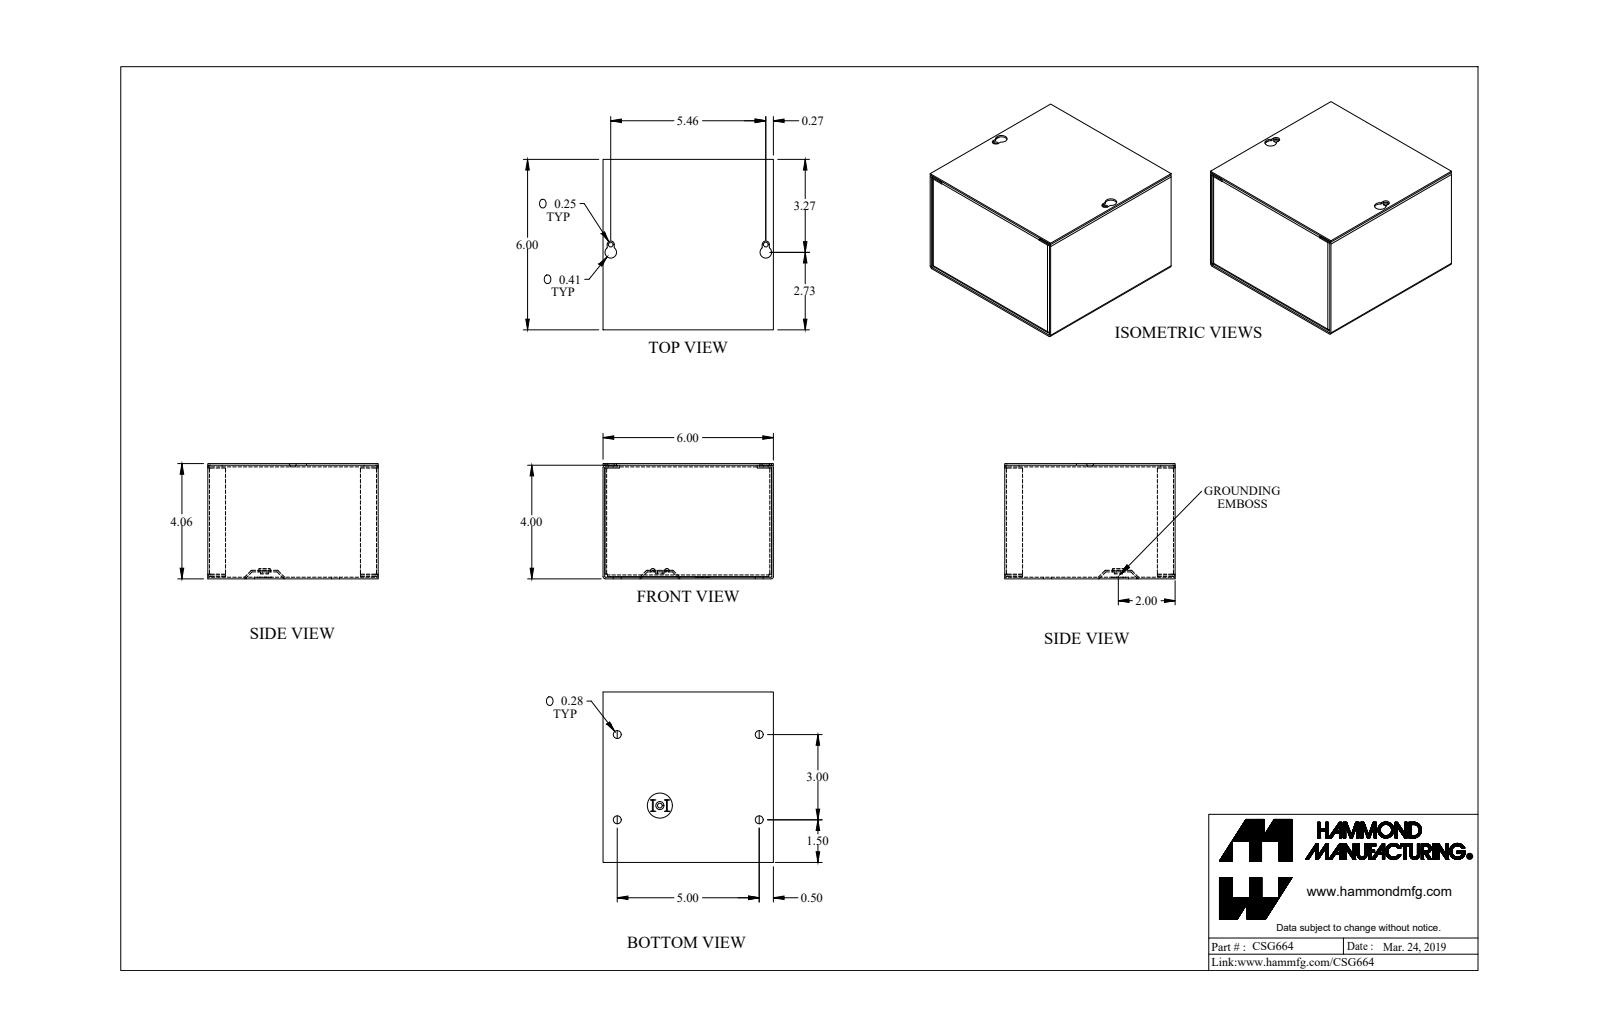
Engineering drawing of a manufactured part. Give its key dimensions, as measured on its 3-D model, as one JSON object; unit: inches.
{"part_name": "CSG664_Default", "step_written_by": "SolidWorks 2019 (CONFIG_CONTROL_DESIGN)", "units": "inches", "bodies": {"solids": 4, "faces": 189, "planar": 121, "cylindrical": 60, "other": 8}, "overall_size": [6, 6, 4.057], "volume_in3": 10.71, "surface_area_in2": 382.8, "round_holes": [[0.281, 4], [0.17, 3], [0.5, 1]], "round_bosses_or_shafts": [[0.492, 1], [0.284, 1]], "partial_cylinders_radius": [[0.029, 12], [0.086, 12], [0.057, 8], [0.125, 2], [0.203, 2]], "face_to_face_distances": [0.057, 5.943, 4, 6, 5.886, 3.943, 4.057, 0.07, 5.873, 0.08], "hole_center_spacings": [1.517, 5.441, 3, 5, 5.831, 1.5, 1.581, 1.998]}
